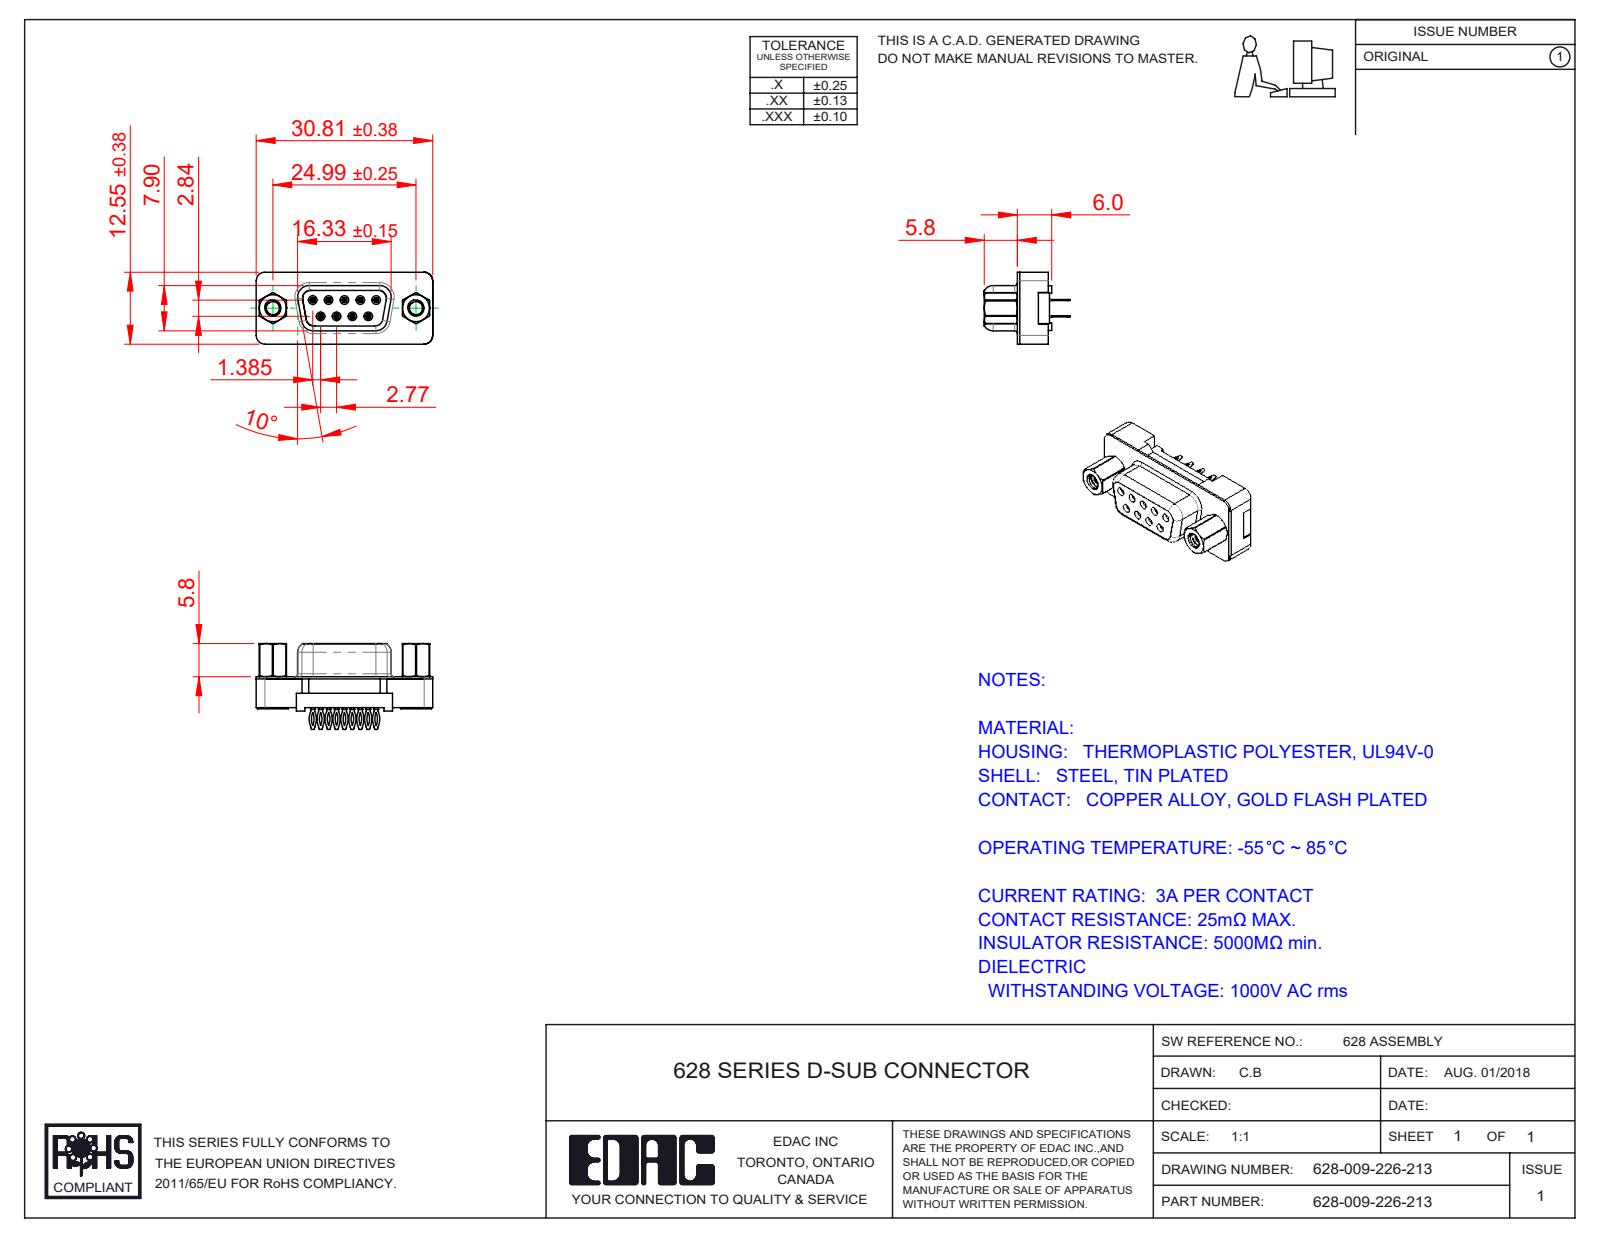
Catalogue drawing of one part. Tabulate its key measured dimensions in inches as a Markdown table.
| quantity | value |
| --- | --- |
| part name | 628 4-40 Hex Standoff; 628 PB 4-40 Threaded Rivet; 628 PB Contact Row 1_26; 628-009-226-213 (+3 more) |
| STEP written by | SolidWorks 2020 (CONFIG_CONTROL_DESIGN) |
| units | inches |
| bodies | 15 solids, 1181 faces (454 planar, 356 cylindrical, 371 other) |
| overall size | 1.213 × 0.591 × 0.494 |
| volume | 0.132 in³ |
| surface area | 7.497 in² |
| round holes (diameter × count) | 0.035 × 9, 0.089 × 2, 0.09 × 2, 0.12 × 2, 0.157 × 2, 0.189 × 2, 0.197 × 2 |
| round bosses / shafts (diameter × count) | 0.193 × 2, 0.11 × 2 |
| partial cylindrical surfaces (radius × count) | 0.01 × 36, 0.115 × 18, 0.131 × 18, 0.02 × 13, 0.053 × 11, 0.012 × 9, 0.059 × 8, 0.035 × 4 |
| main face-to-face distances | 0.016, 0.079, 0.218, 0.109, 0.098, 0.197, 0.244, 0.213, 0.343, 0.297 |
| hole center spacings | 0.124, 0.109, 0.218, 0.198, 0.198, 0.327, 0.28, 0.294 |
